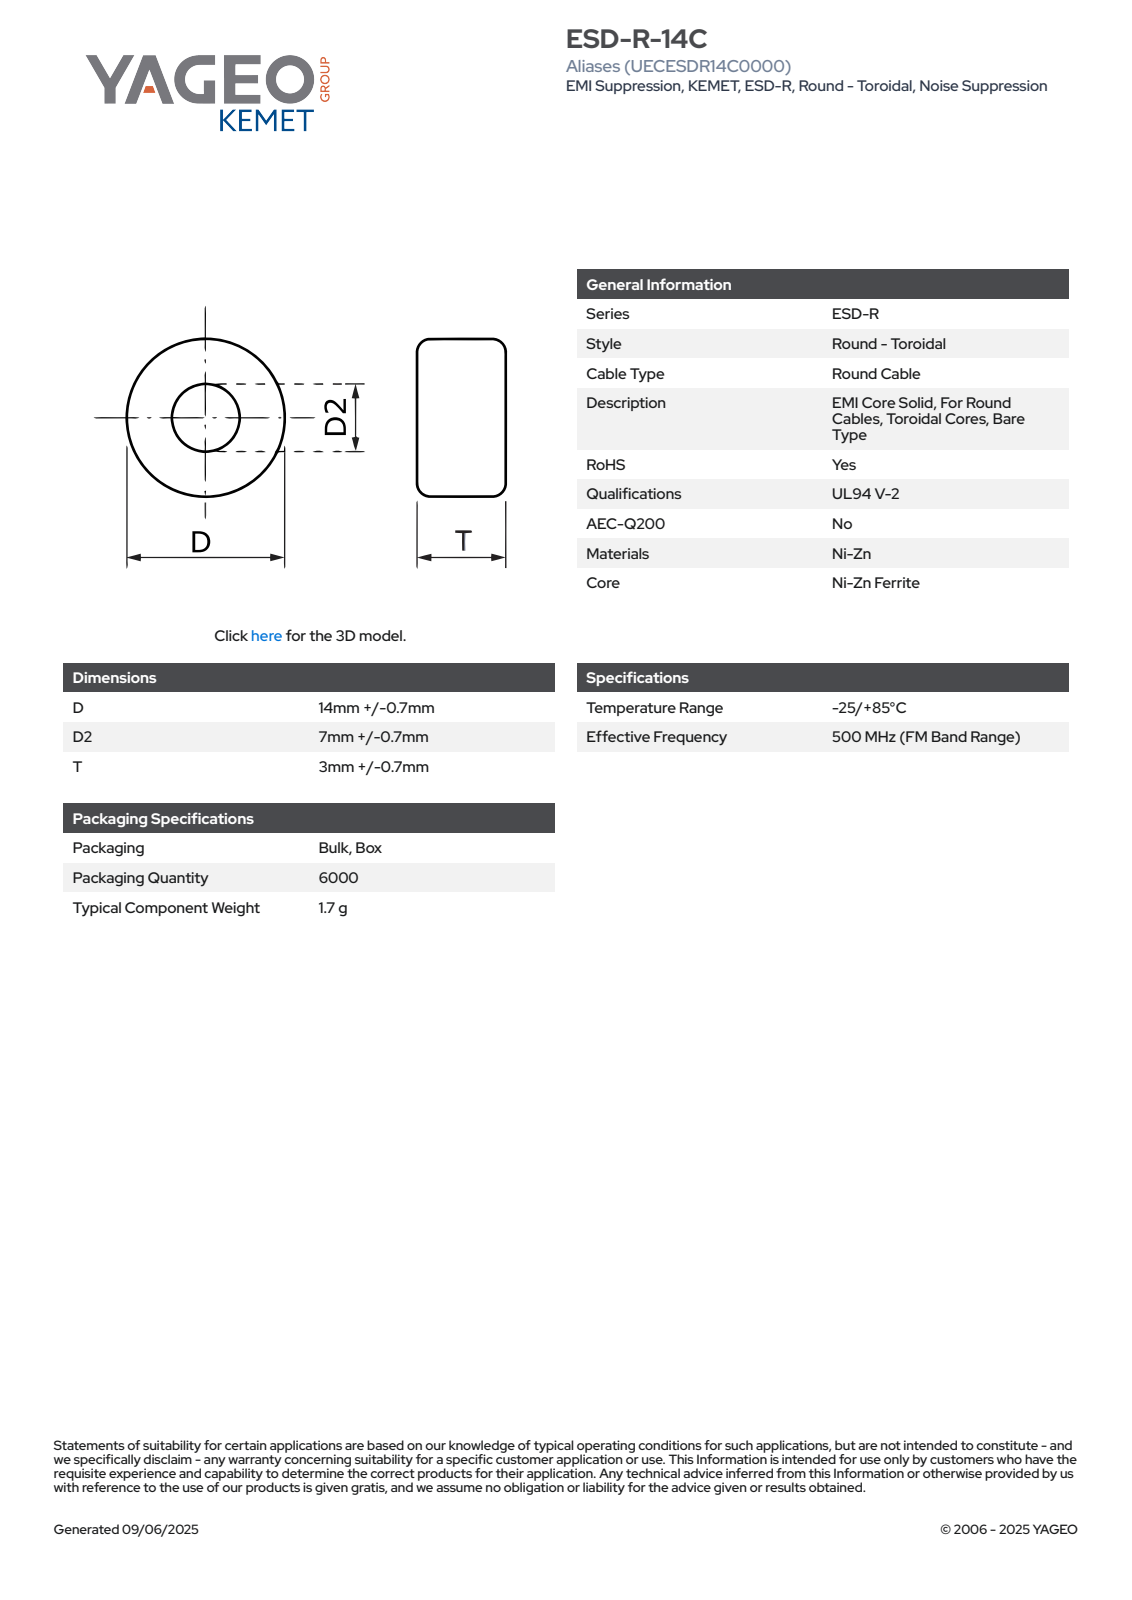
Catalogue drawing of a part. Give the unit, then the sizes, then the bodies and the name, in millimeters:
Units: millimetres
Overall size (bounding box): 14.71 × 14.7 × 3.7
Round holes (diameter × count): ⌀7 ×1
Round bosses / shafts (diameter × count): ⌀14.7 ×1
Partial cylindrical surfaces — rounded edges, fillets, slot ends (radius × count): R7.36 ×1
Main face-to-face distances: 3.7, 1, 2.7, 1.7, 0.32, 1.32, 2.38, 1.38, 1.06, 2.06
Volume: 481 mm³ · Surface area: 499 mm²
Bodies: 1 solid, 66 faces (24 planar, 7 cylindrical, 35 other)
Part name (STEP PRODUCT): EC_KBC_D14.7D27T3.7
STEP written by: SolidWorks 2021 (AUTOMOTIVE_DESIGN)
